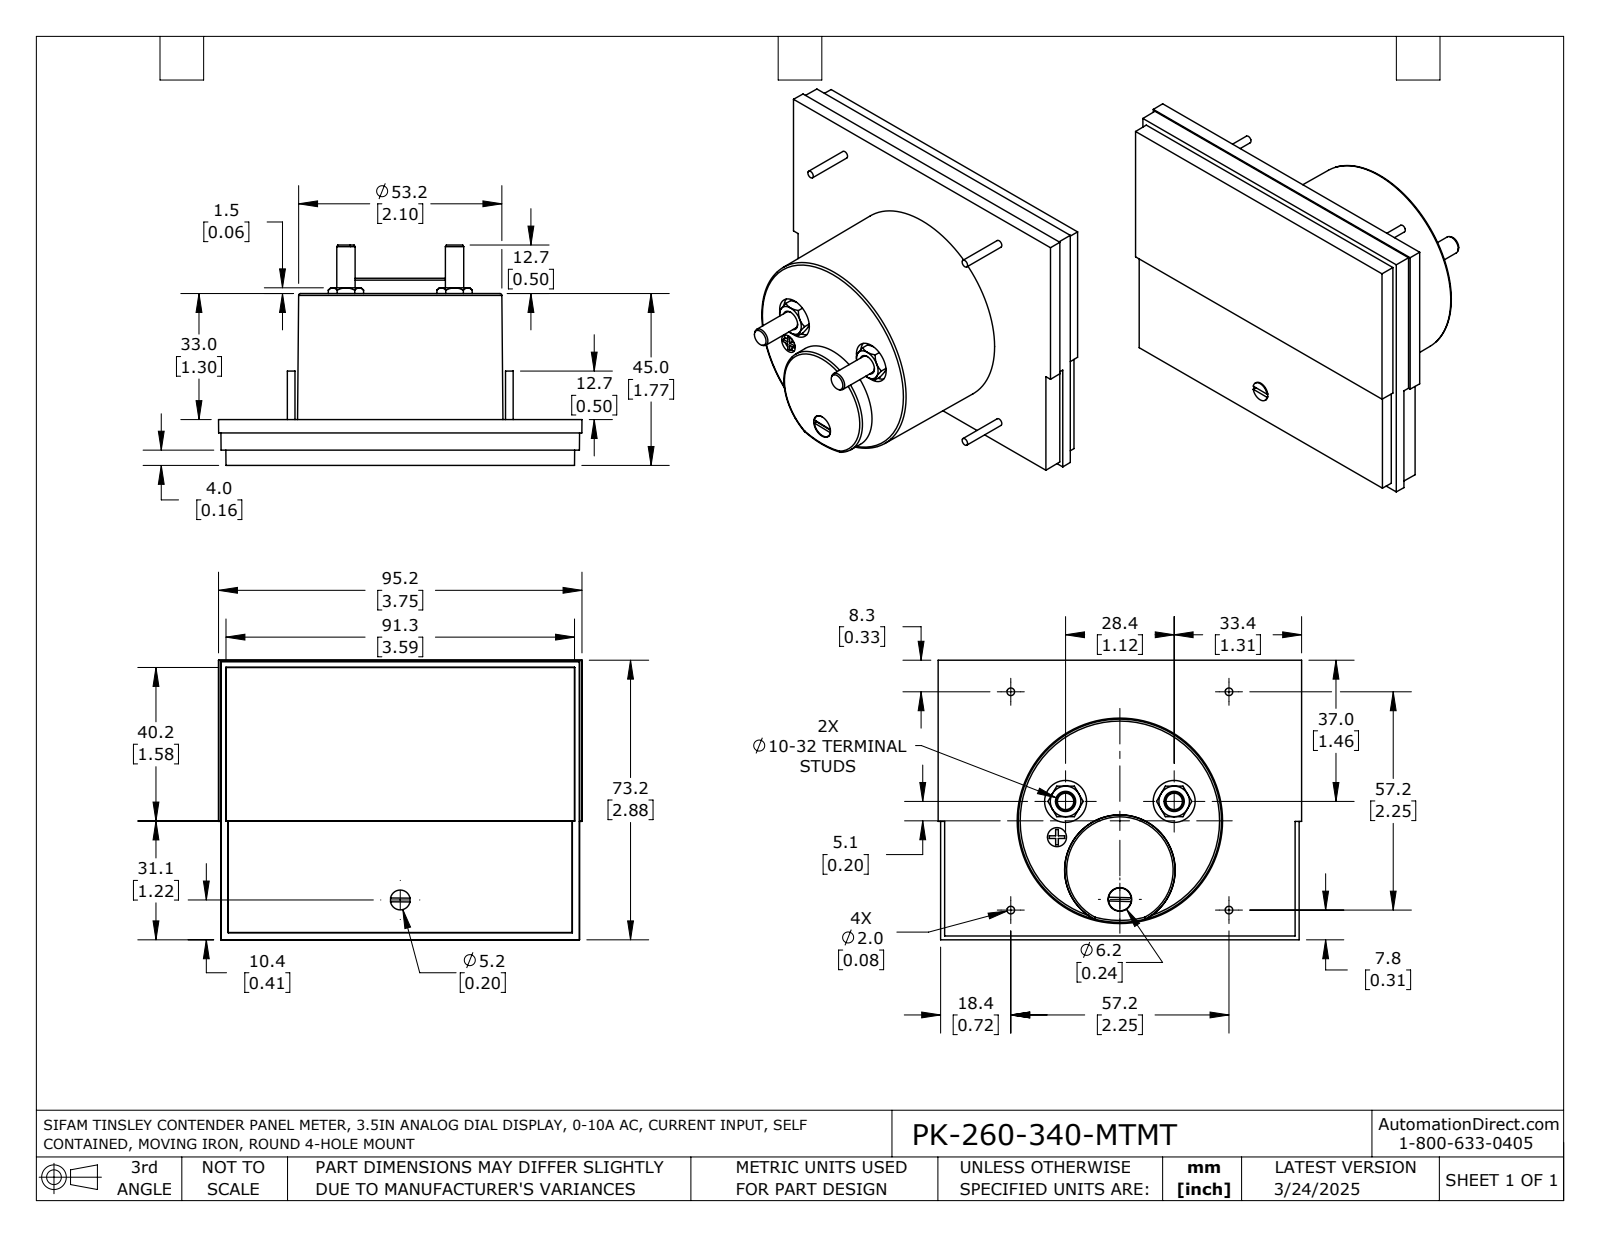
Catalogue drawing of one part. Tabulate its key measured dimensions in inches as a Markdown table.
| quantity | value |
| --- | --- |
| part name | PK-260-340-MTMT |
| STEP written by | SolidWorks 2021 (AUTOMOTIVE_DESIGN) |
| units | inches |
| bodies | 1 solid, 163 faces (76 planar, 31 cylindrical, 56 other) |
| overall size | 3.748 × 2.882 × 2.272 |
| volume | 9.446 in³ |
| surface area | 38.39 in² |
| round holes (diameter × count) | 0.433 × 2, 0.197 × 1, 0.244 × 1 |
| round bosses / shafts (diameter × count) | 0.079 × 4, 0.189 × 2, 0.236 × 1, 0.205 × 1 |
| partial cylindrical surfaces (radius × count) | 0.1 × 1 |
| main face-to-face distances | 0.472, 0.03, 0.443, 1.772, 1.299, 1.742, 0.157, 0.073, 0.315, 1.457 |
| hole center spacings | 1.155, 0.379, 0.912, 1.12, 1.263 |
